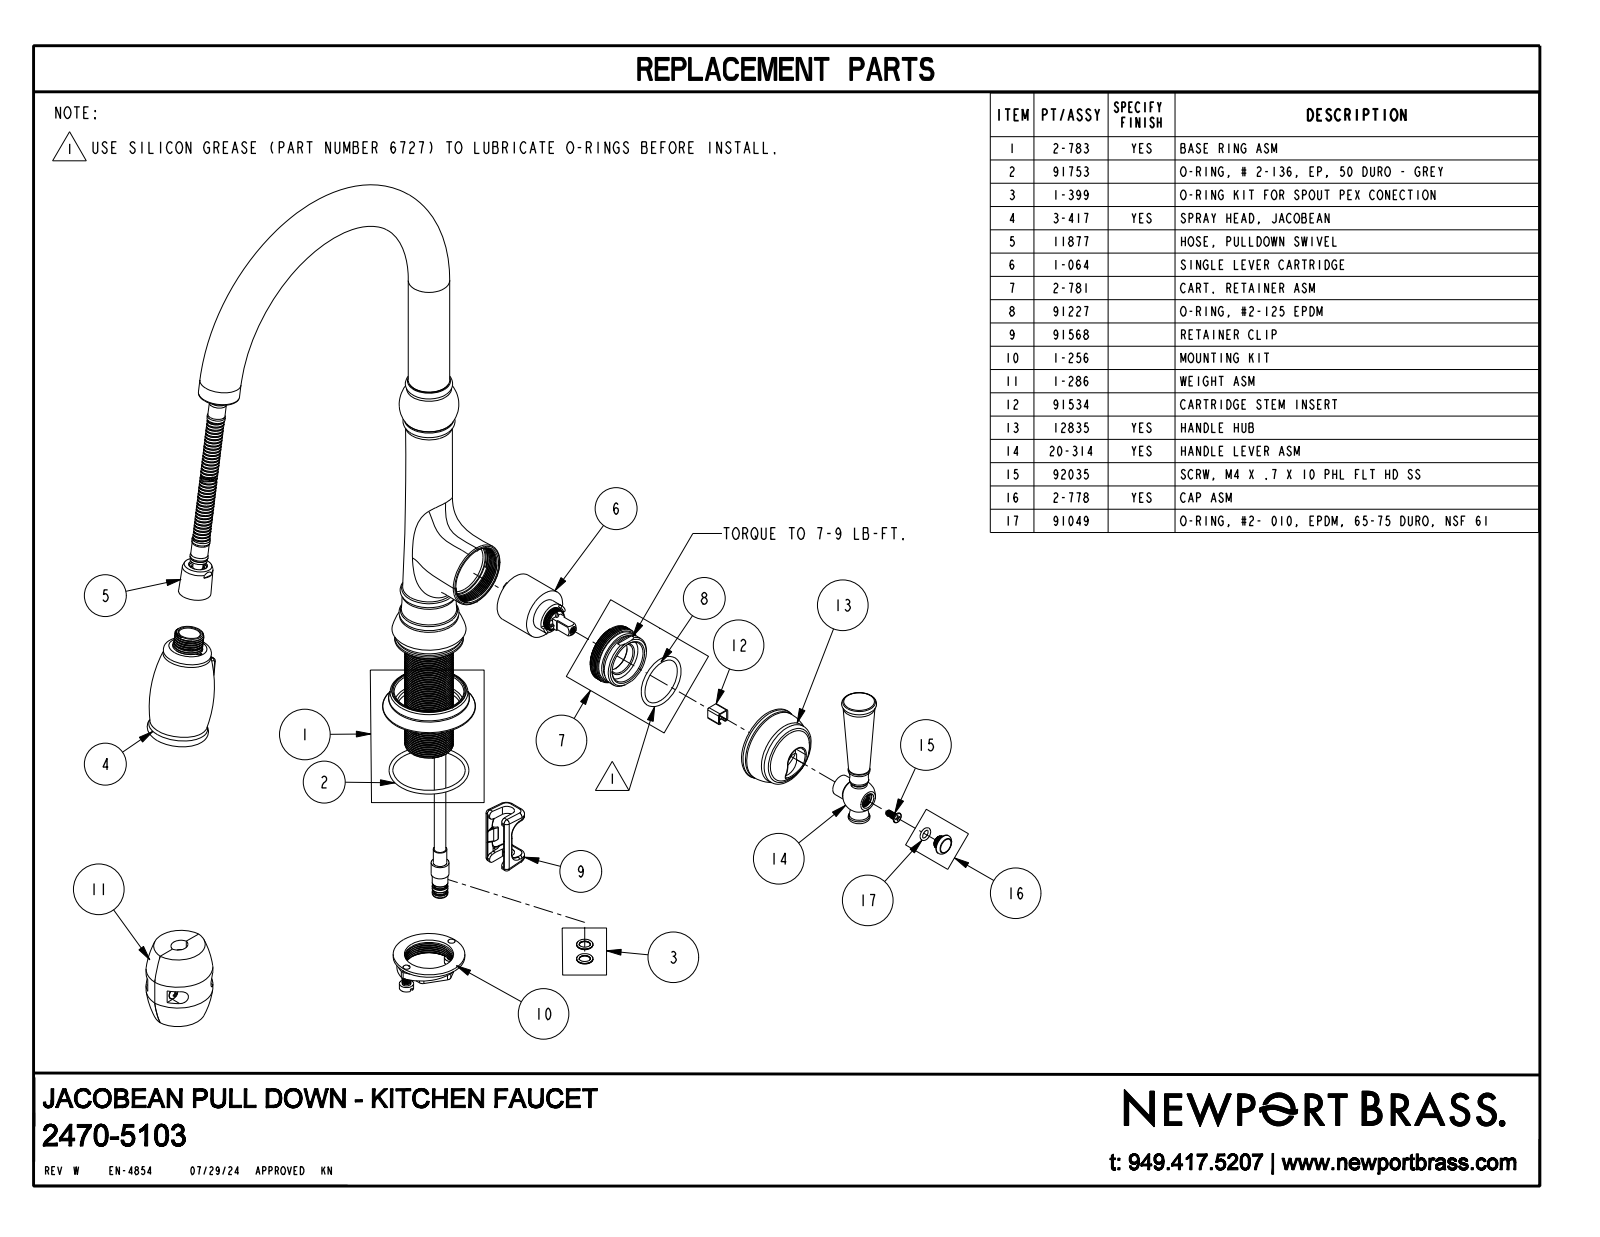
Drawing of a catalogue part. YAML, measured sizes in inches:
part_name: "2470-5103"
step_written_by: "CREO PARAMETRIC BY PTC INC, 2018400 (CONFIG_CONTROL_DESIGN)"
units: inches
bodies: {solids: 1, faces: 363, planar: 62, cylindrical: 32, other: 269}
overall_size: [16.935, 10.674, 4.909]
volume: 44.5
surface_area: 147.1
round_holes:
  - {diameter: 0.563, count: 1}
  - {diameter: 1.242, count: 1}
round_bosses_or_shafts:
  - {diameter: 2.02, count: 1}
  - {diameter: 1.228, count: 1}
  - {diameter: 1.124, count: 1}
  - {diameter: 1.12, count: 1}
  - {diameter: 0.595, count: 1}
  - {diameter: 0.56, count: 1}
  - {diameter: 0.45, count: 1}
partial_cylinders:
  - {radius: 0.059, count: 4}
  - {radius: 0.08, count: 4}
  - {radius: 0.098, count: 2}
  - {radius: 0.12, count: 2}
  - {radius: 0.337, count: 2}
face_to_face_distances: [0.04, 0.033, 0.795, 2.724, 2.718, 2.684, 0.675, 7.653, 0.041, 0.047]
